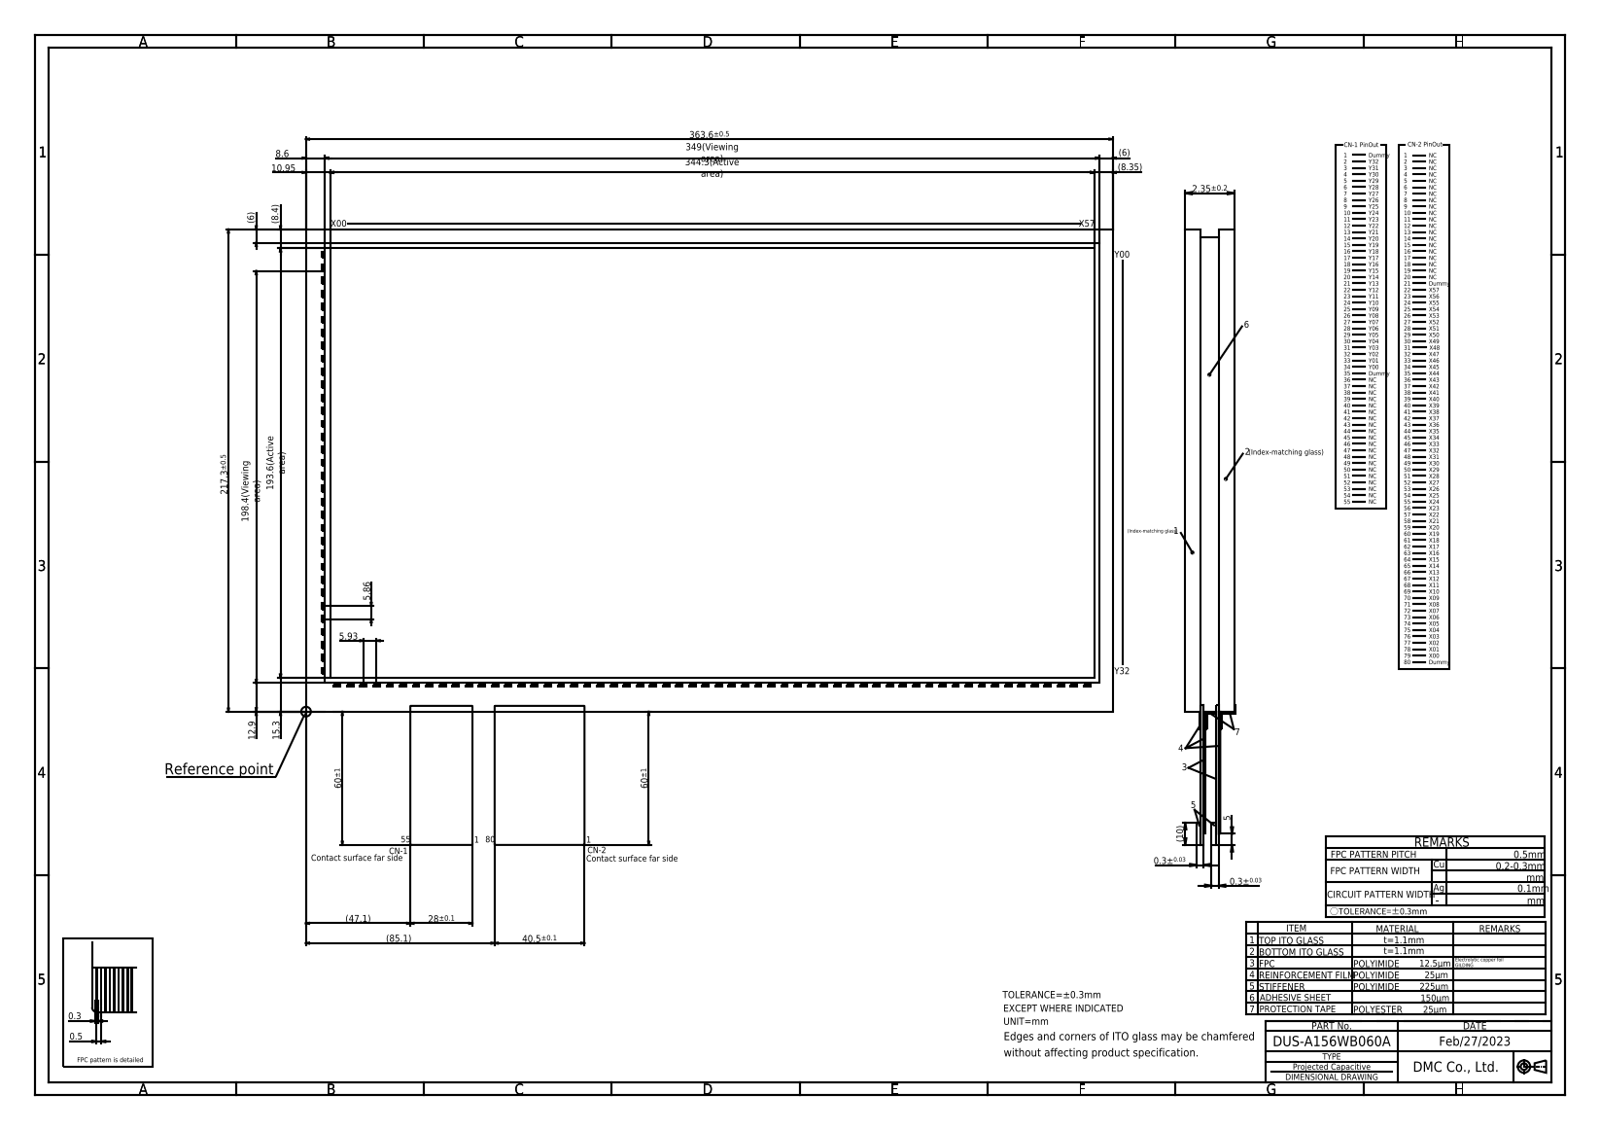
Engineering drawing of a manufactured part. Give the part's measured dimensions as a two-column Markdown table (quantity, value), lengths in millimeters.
| quantity | value |
| --- | --- |
| part name | DUS-A156WB060A |
| STEP written by | Autodesk Inventor 2020 (CONFIG_CONTROL_DESIGN) |
| units | millimeters |
| bodies | 1 solid, 578 faces (574 planar, 4 cylindrical, 0 other) |
| overall size | 509.04 × 320.76 × 2.35 |
| volume | 185 996 mm³ |
| surface area | 169 276 mm² |
| partial cylindrical surfaces (radius × count) | 0.2 × 4 |
| main face-to-face distances | 2.35, 1.1, 1.2, 1.15, 1.25, 1, 2.25, 217.3, 0.8, 0.7 |
